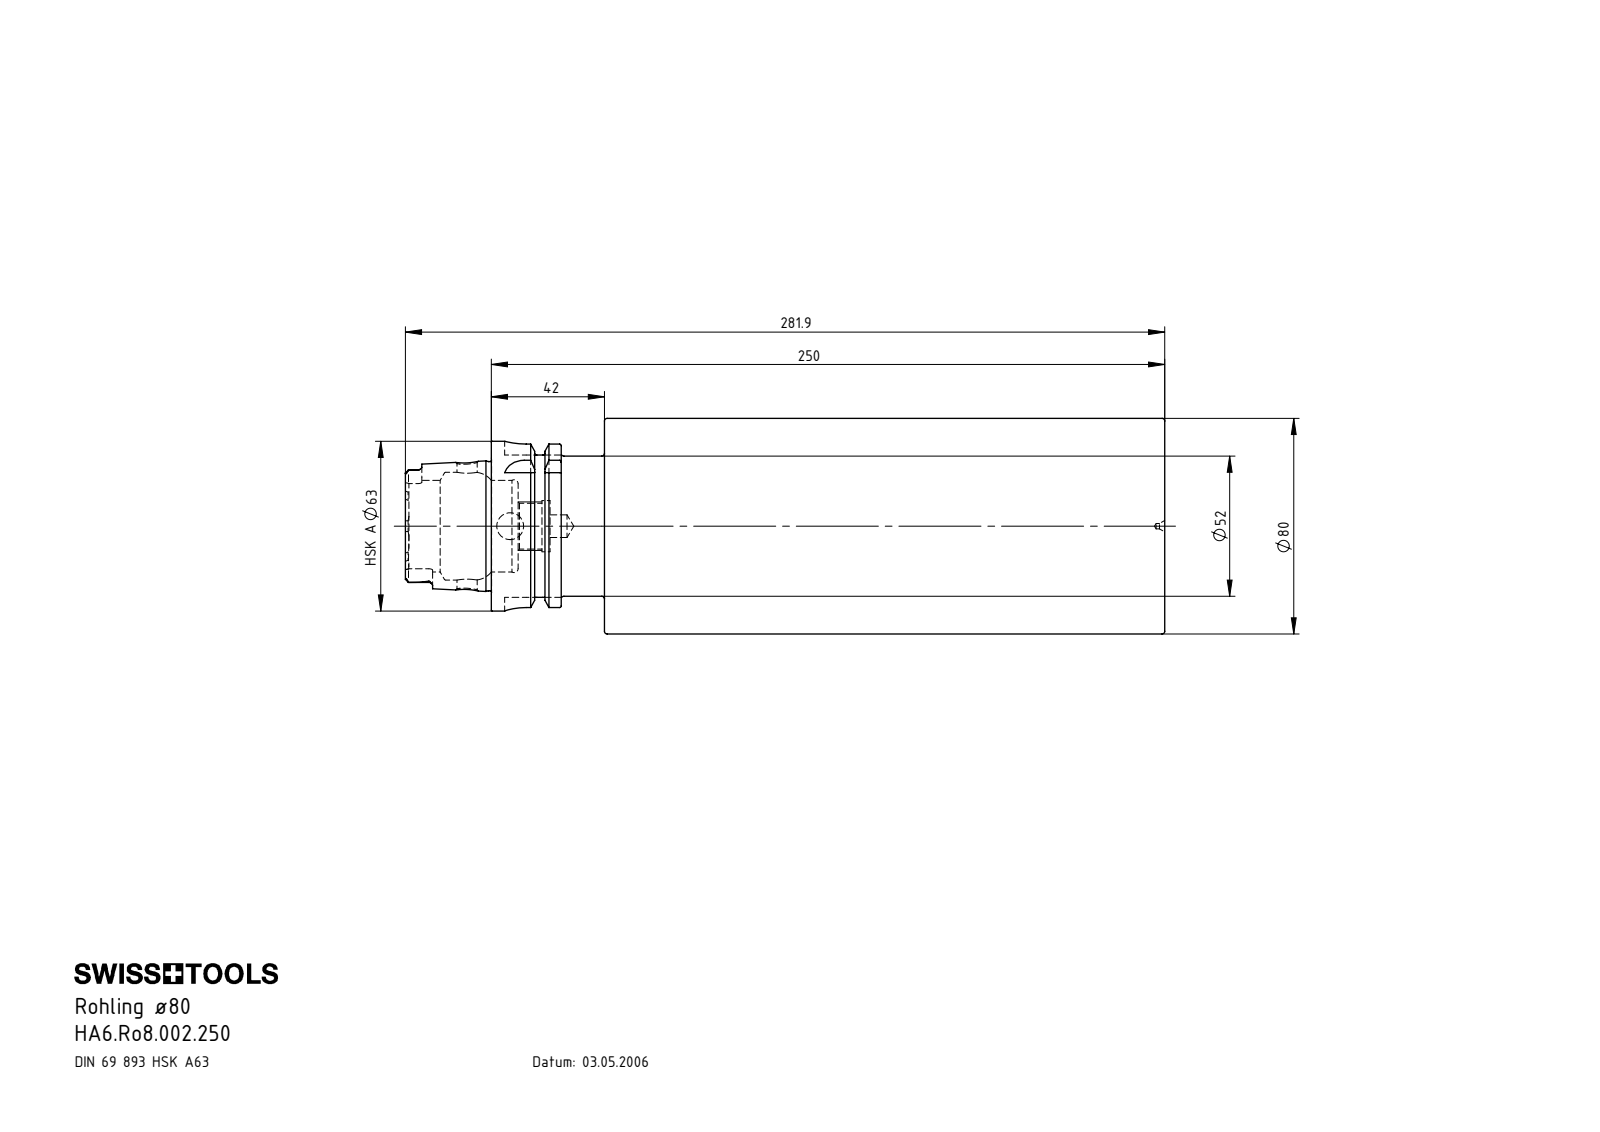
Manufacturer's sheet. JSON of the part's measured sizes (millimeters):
{"part_name": "HA6.Ro8.002.250", "step_written_by": "SolidWorks 2017 (AUTOMOTIVE_DESIGN)", "units": "millimeters", "bodies": {"solids": 1, "faces": 180, "planar": 48, "cylindrical": 49, "other": 83}, "overall_size": [281.9, 80, 80], "volume_mm3": 1161000, "surface_area_mm2": 82760, "round_holes": [[2, 1], [7.5, 1], [8.4, 1], [10, 1], [17, 1], [19, 1], [34, 1], [40, 1]], "round_bosses_or_shafts": [[80, 1], [63, 1], [54.95, 1], [52, 1], [47.94, 1]], "partial_cylinders_radius": [[1.4, 6], [2.88, 4], [8, 4]], "face_to_face_distances": [208, 42, 250, 25.95, 16.05, 224.05, 16, 9.95, 32.05, 240.05]}
